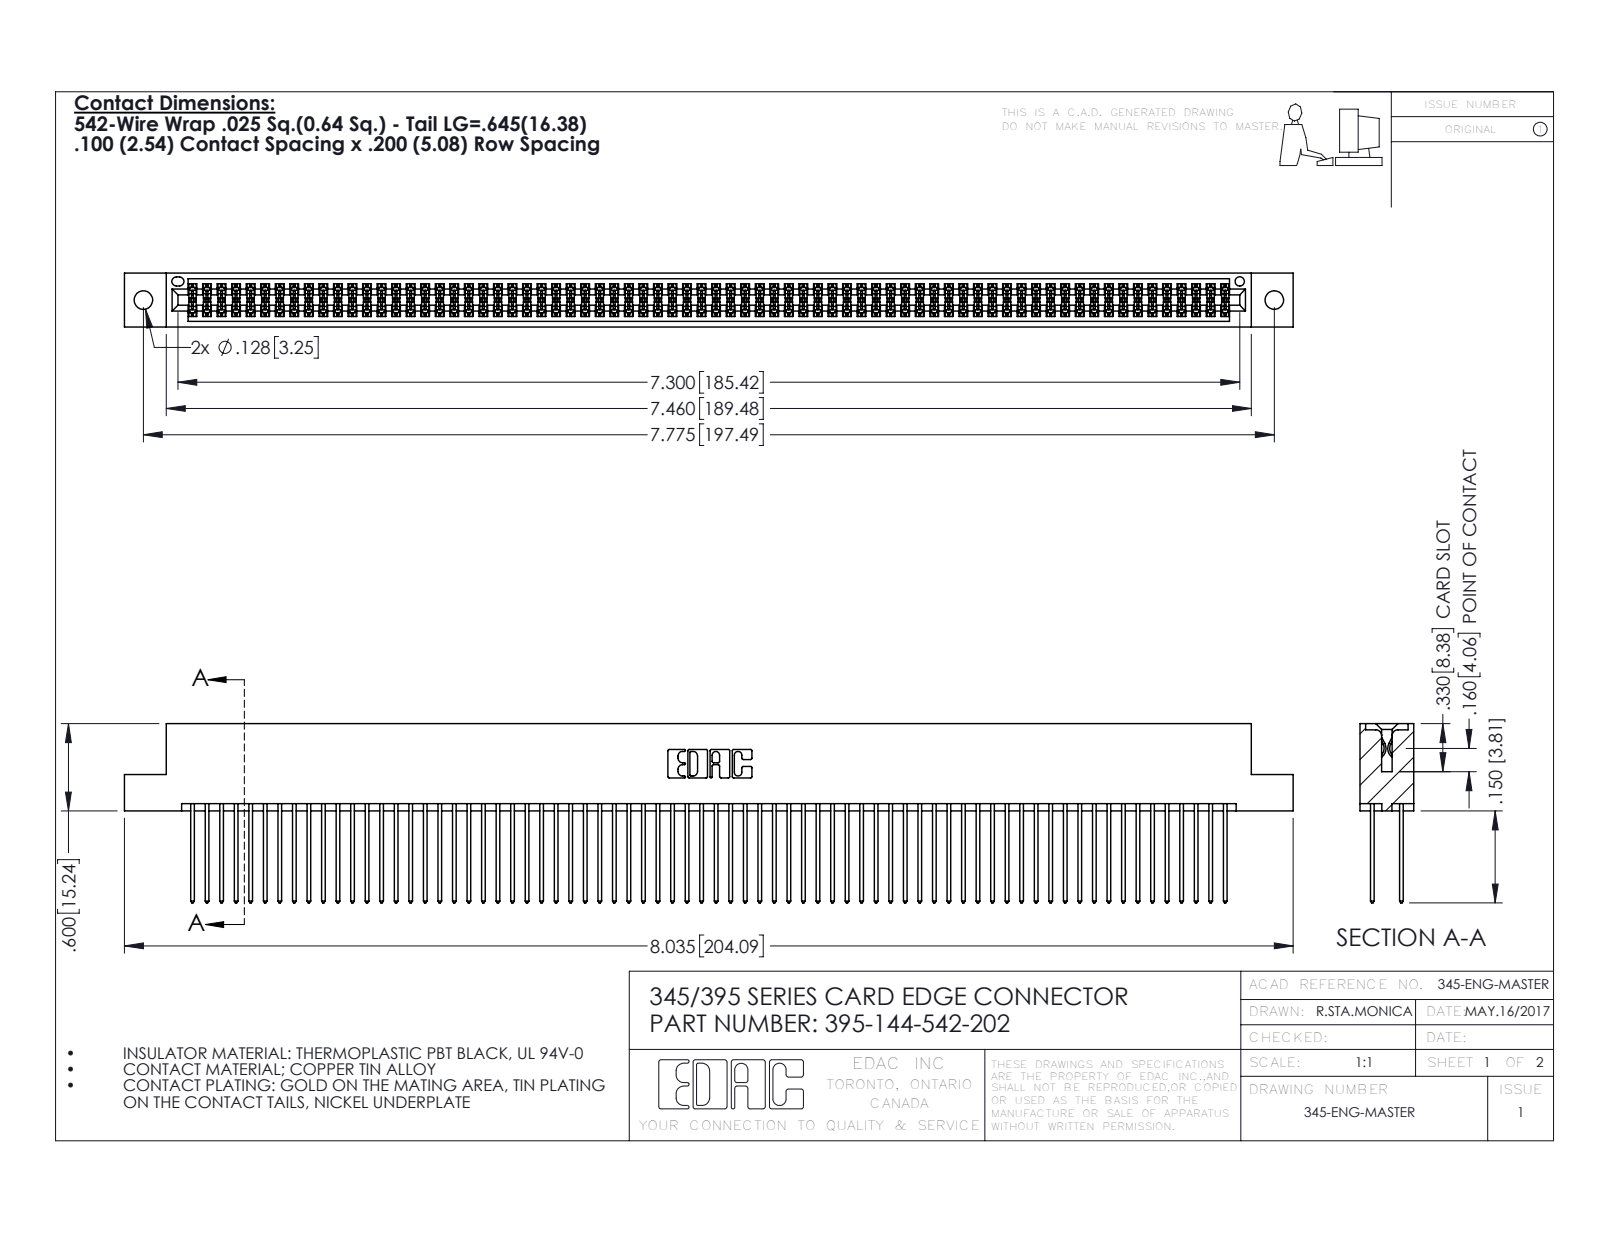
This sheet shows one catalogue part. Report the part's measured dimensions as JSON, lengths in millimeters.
{"part_name": "345 Part_Flush Mounting Lugs - 0.128 Dia; 345-292-001_345-293-142; 395-144-542-202", "step_written_by": "SolidWorks 2016 (CONFIG_CONTROL_DESIGN)", "units": "millimeters", "bodies": {"solids": 145, "faces": 7326, "planar": 4832, "cylindrical": 2494, "other": 0}, "overall_size": [204.1, 31.3, 9.4], "volume_mm3": 20750, "surface_area_mm2": 34100, "round_holes": [[3.3, 2], [1.6, 1]], "partial_cylinders_radius": [[0.2, 216], [0.3, 144], [0.3, 22], [0.2, 6], [0.8, 6], [0.7, 3], [0.4, 2], [0.5, 2]], "face_to_face_distances": [7.6, 1.8, 5.1, 2.5, 6.9, 0.6, 5.7, 9.4, 4.4, 3.8], "hole_center_spacings": [6.9, 191.5, 197.5]}
